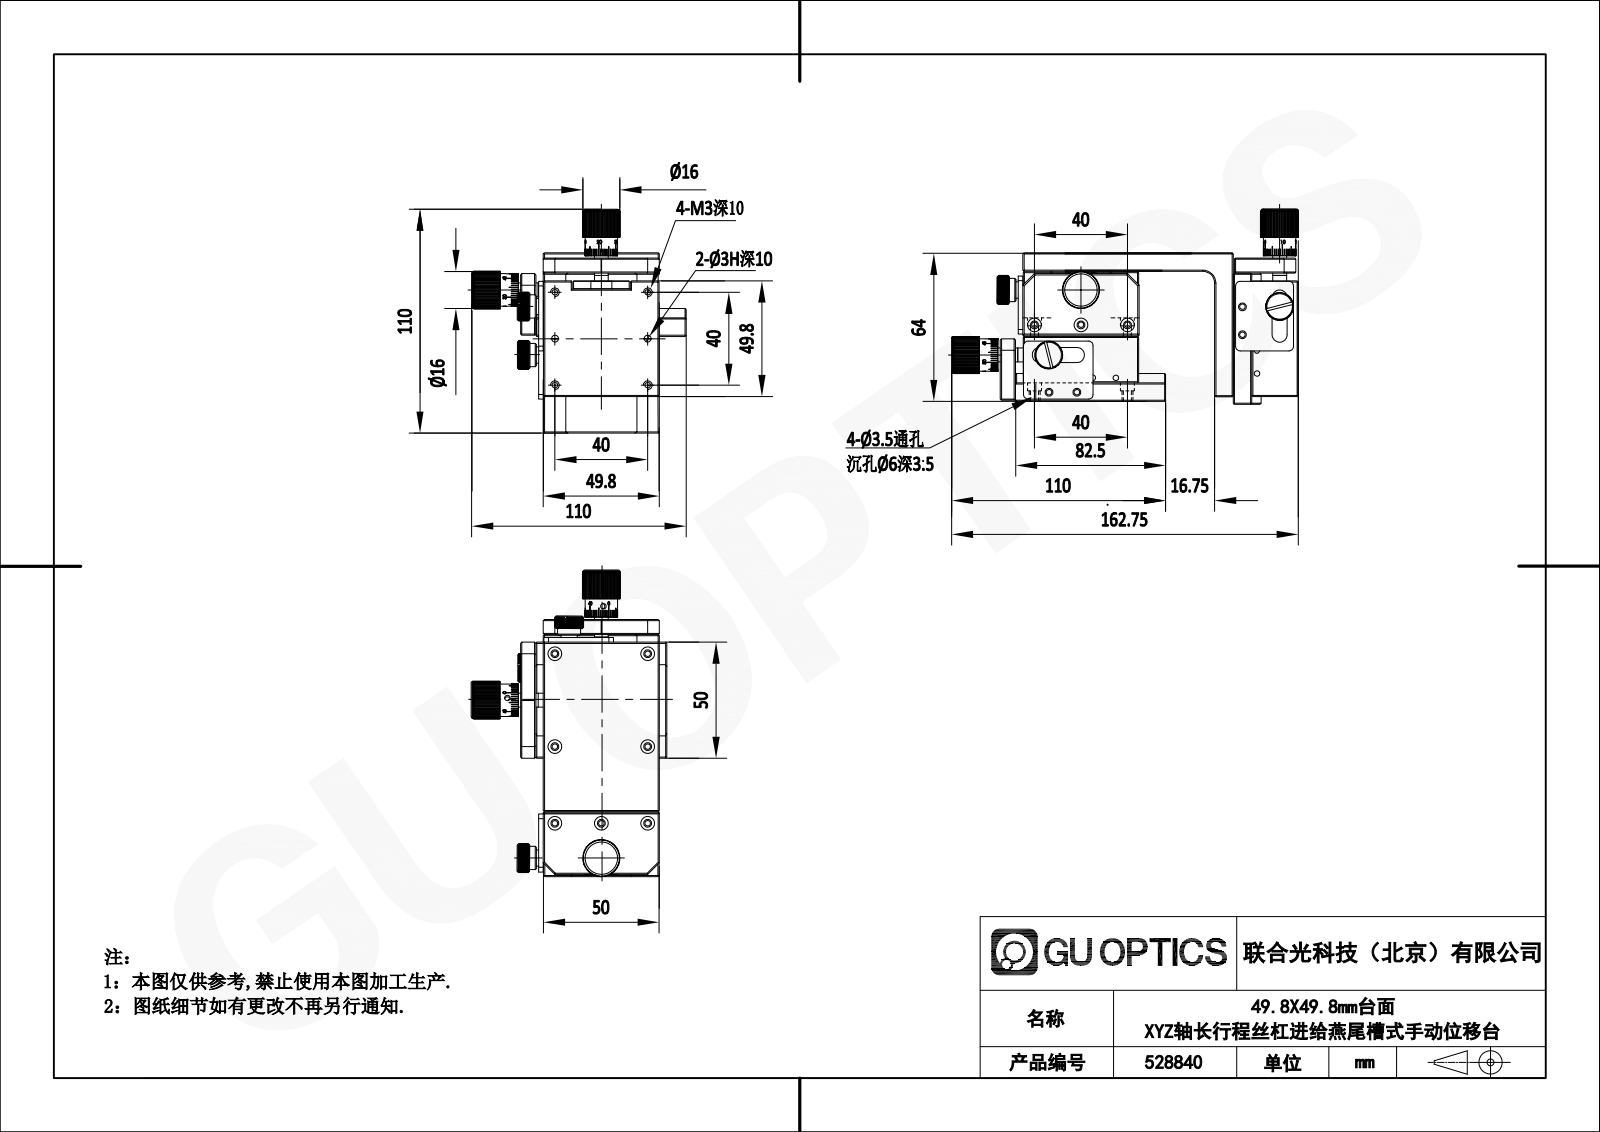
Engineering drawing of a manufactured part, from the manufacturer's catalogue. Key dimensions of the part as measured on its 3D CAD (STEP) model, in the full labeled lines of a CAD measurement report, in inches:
Part name (STEP PRODUCT): 528840
STEP written by: SolidWorks 2020 (CONFIG_CONTROL_DESIGN)
Units: inches
Bodies: 7 solids, 2566 faces (1350 planar, 1072 cylindrical, 144 other)
Overall size (bounding box): 6.407 × 4.331 × 4.331
Volume: 21.11 in³ · Surface area: 181.9 in²
Round holes (diameter × count): ⌀0.079 ×28, ⌀0.138 ×23, ⌀0.236 ×17, ⌀0.098 ×15, ⌀0.048 ×12, ⌀0.118 ×8, ⌀0.097 ×6, ⌀0.134 ×4, ⌀0.079 ×3, ⌀0.163 ×3, ⌀0.256 ×3, ⌀0.394 ×3
Round bosses / shafts (diameter × count): ⌀0.551 ×3, ⌀0.394 ×3, ⌀0.354 ×3, ⌀0.276 ×3, ⌀0.236 ×3, ⌀0.235 ×3, ⌀0.234 ×3, ⌀0.197 ×3
Partial cylindrical surfaces — rounded edges, fillets, slot ends (radius × count): R0.079 ×12, R0.128 ×6, R0.295 ×6, R0.228 ×3, R0.236 ×3, R0.303 ×3, R0.315 ×3, R0.197 ×1
Main face-to-face distances: 1.102, 0.315, 0.787, 0.63, 1.417, 0.157, 0.472, 1.965, 2.205, 0.945
Hole centre spacings: 0.394, 0.787, 0.984, 1.761, 1.575, 0.278, 0.557, 1.113
